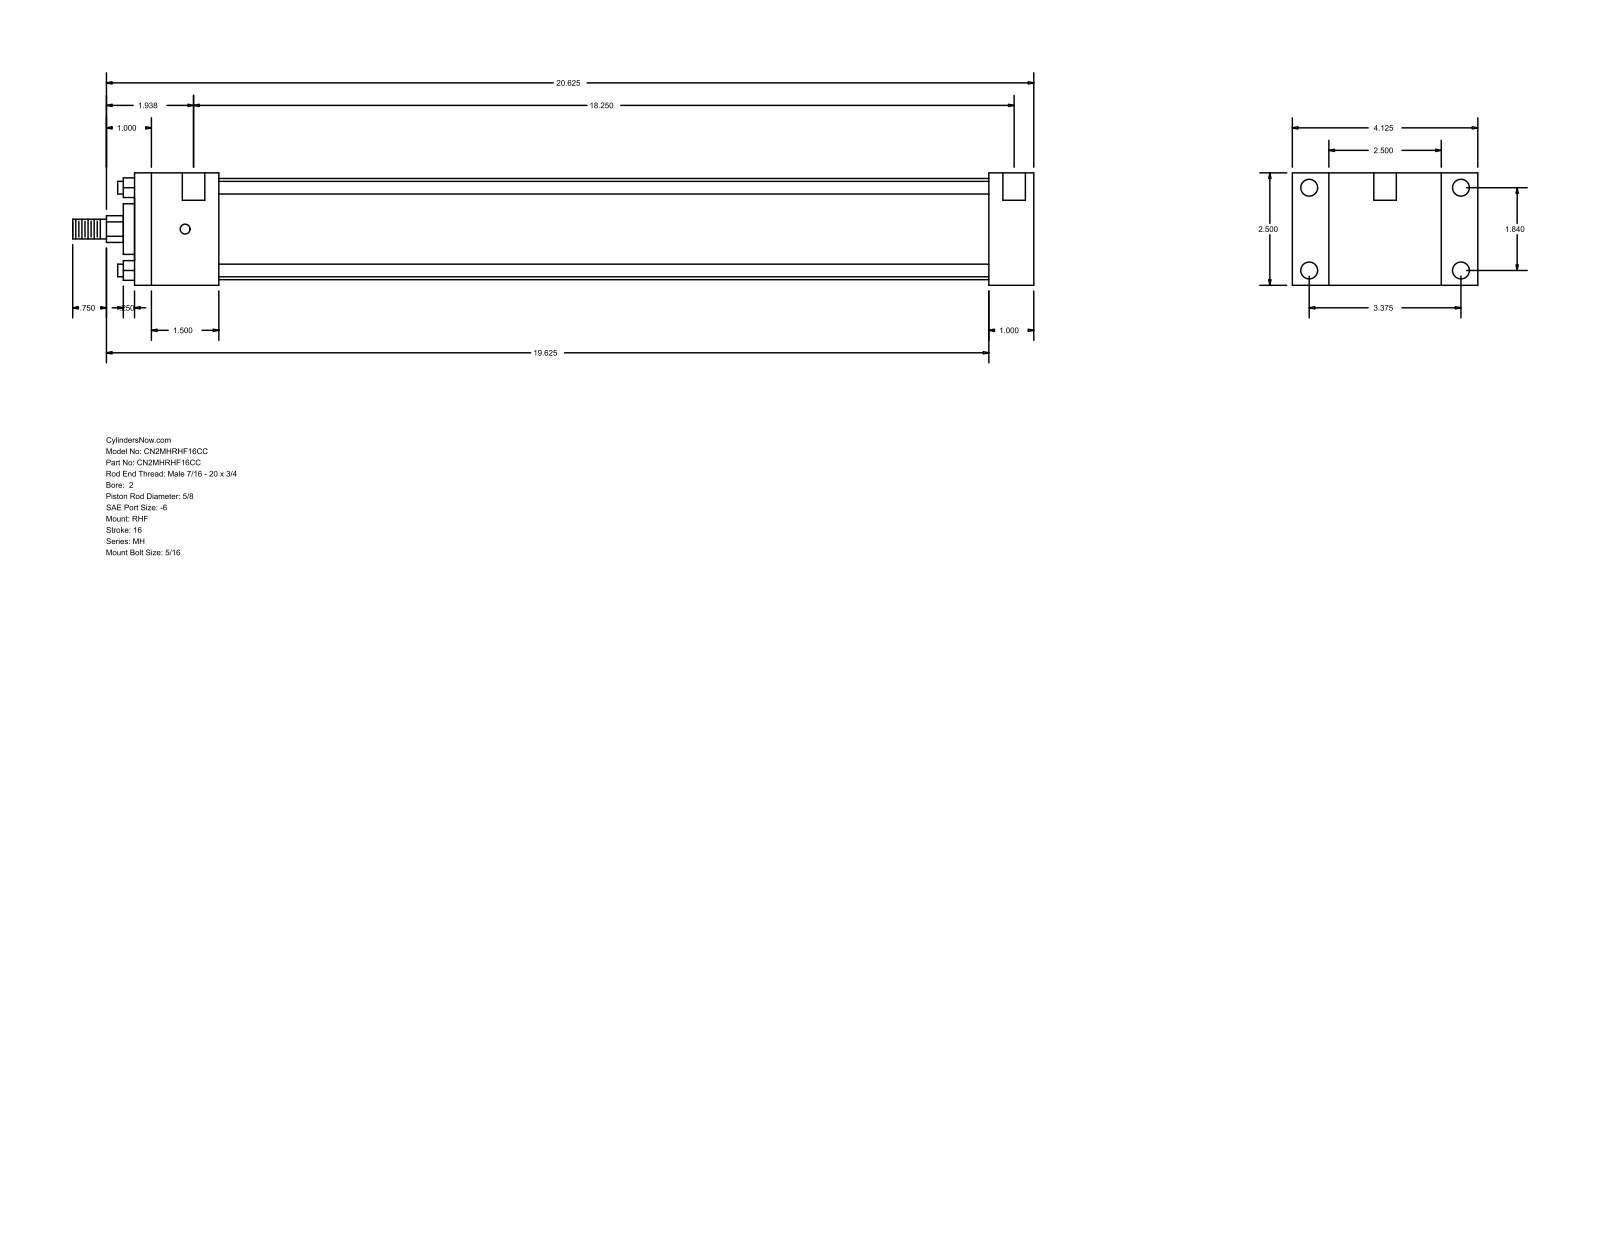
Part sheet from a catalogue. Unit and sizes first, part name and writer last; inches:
Units: inches
Overall size (bounding box): 21.375 × 4.125 × 2.5
Round holes (diameter × count): ⌀0.219 ×4, ⌀0.375 ×4, ⌀0.5 ×2
Round bosses / shafts (diameter × count): ⌀0.281 ×4, ⌀2.25 ×1, ⌀1.125 ×1, ⌀0.625 ×1, ⌀0.437 ×1
Partial cylindrical surfaces — rounded edges, fillets, slot ends (radius × count): R0.297 ×1
Main face-to-face distances: 2.5, 1, 0.813, 3.313, 19, 20, 4.125, 1.875, 17.125, 18.125
Hole centre spacings: 1.84, 3.375, 3.844, 18.563, 0.125, 0.187, 18.25, 18.375
Bodies: 0 solids, 88 faces (60 planar, 28 cylindrical, 0 other)
Part name (STEP PRODUCT): MH_RHF__0200_0.625
STEP written by: GSSL Pune (CONFIG_CONTROL_DESIGN)
